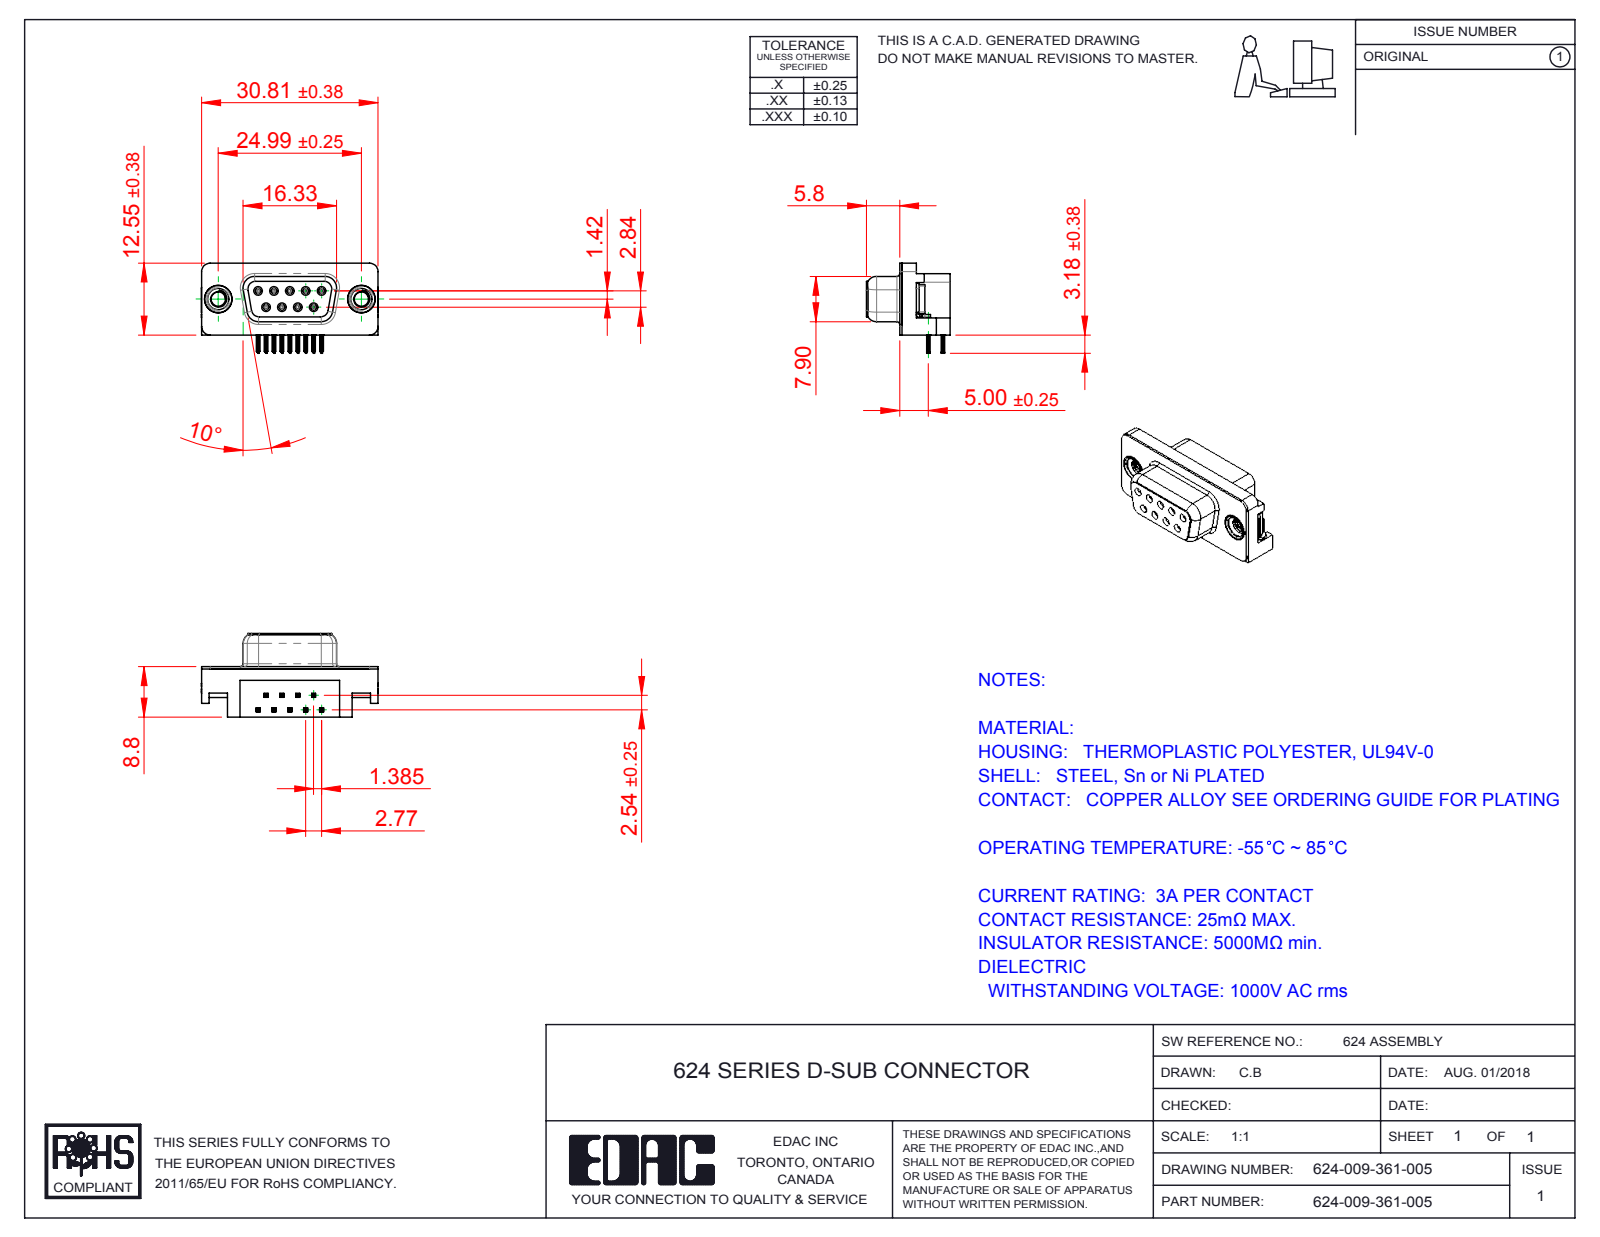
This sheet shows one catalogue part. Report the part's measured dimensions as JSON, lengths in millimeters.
{"part_name": "624 Contact Top; 624 Non Board Mount; 624 M3 Threaded Rivet; 624 Socket Bottom (+3 more)", "step_written_by": "SolidWorks 2016 (CONFIG_CONTROL_DESIGN)", "units": "millimeters", "bodies": {"solids": 15, "faces": 1520, "planar": 642, "cylindrical": 410, "other": 468}, "overall_size": [30.89, 15.73, 14.6], "volume_mm3": 2932, "surface_area_mm2": 4338, "round_holes": [[0.8, 9], [0.9, 9], [2.5, 2], [4, 2], [4.8, 2], [5, 2]], "round_bosses_or_shafts": [[1.2, 9], [4.9, 2], [4.75, 2], [3.9, 2]], "partial_cylinders_radius": [[0.1, 72], [0.15, 36], [0.35, 18], [1, 18], [0.34, 9], [0.25, 8], [1.35, 8], [1.5, 7]], "face_to_face_distances": [0.4, 8.4, 8.8, 2.9, 2.5, 6.2, 5.9, 0.35, 10.69, 10.34], "hole_center_spacings": [3.16, 2.77, 5.54, 5.03, 5.04, 8.31, 7.48, 7.49]}
